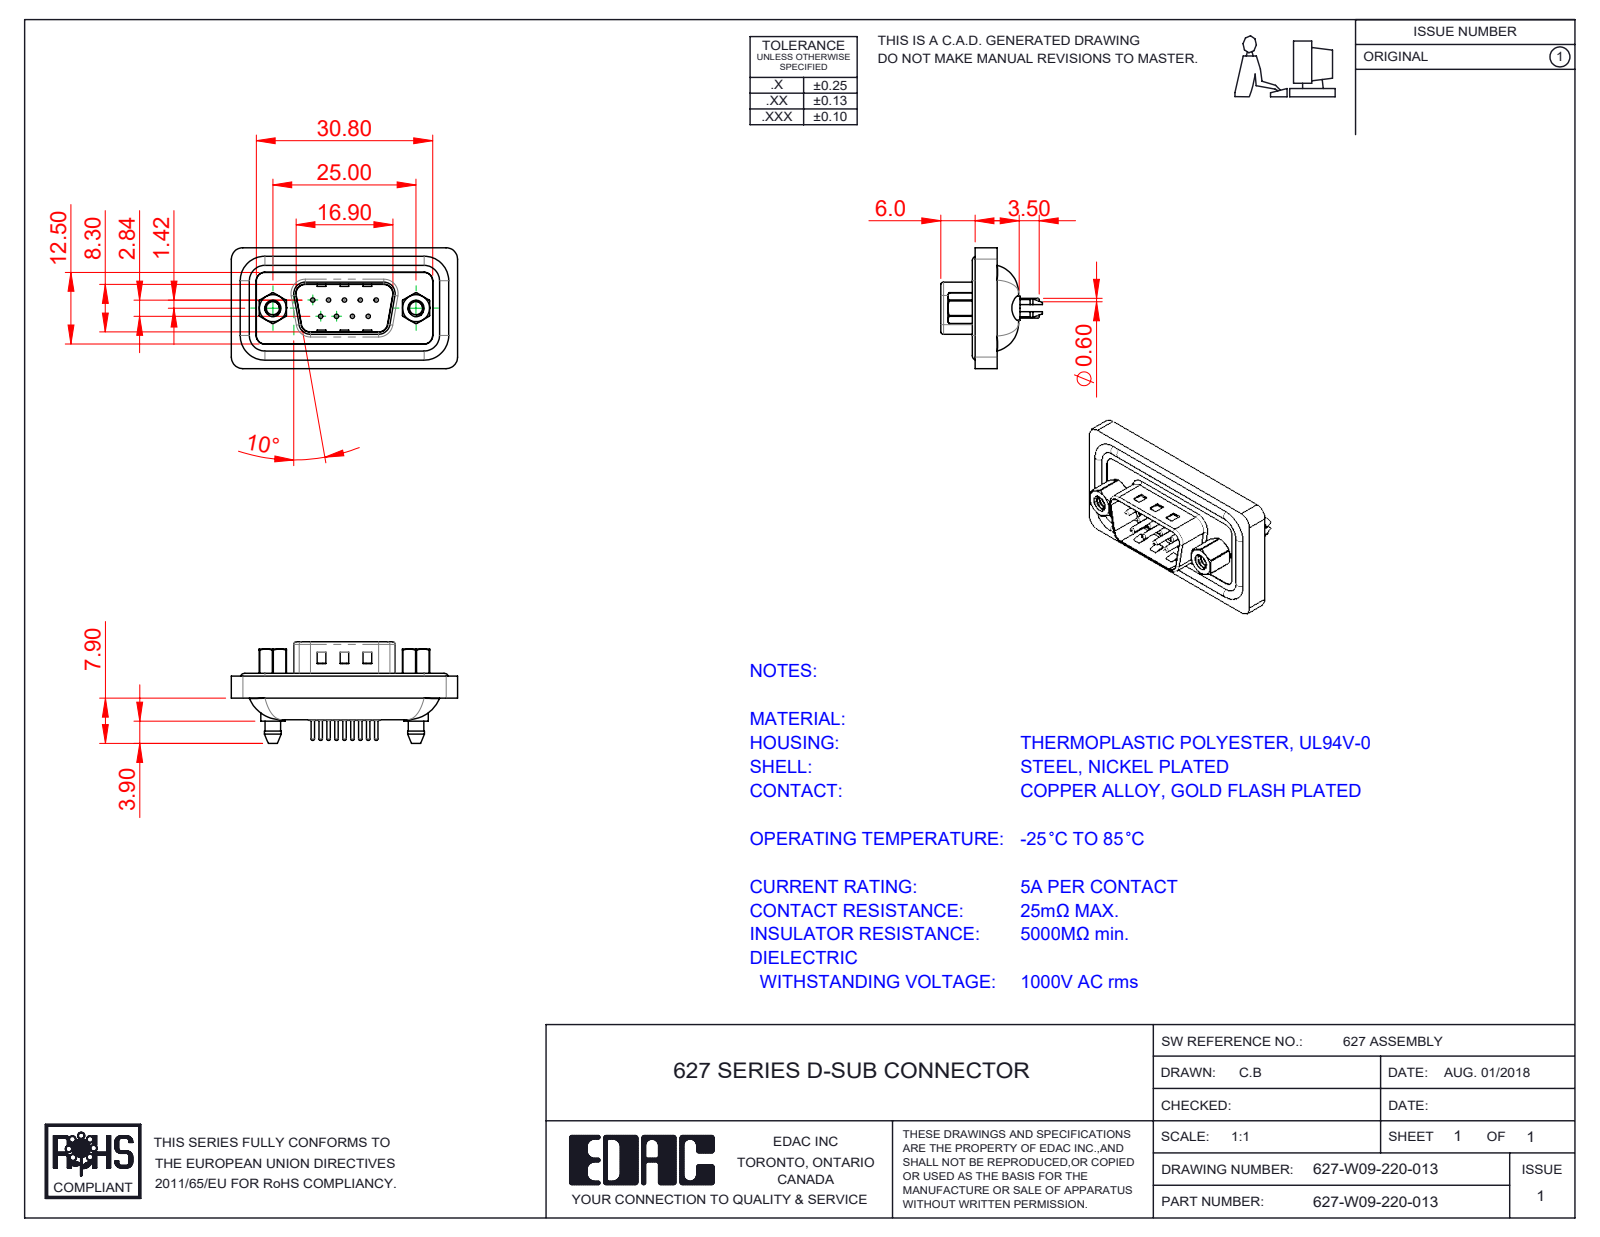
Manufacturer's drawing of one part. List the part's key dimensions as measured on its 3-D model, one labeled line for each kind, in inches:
Part name (STEP PRODUCT): 627W 4-40 Hex Standoff; 627W Contact Row 2_20; 627W Waterproof Housing_09 Contacts BL; 627W Contact Row 1_20 (+4 more)
STEP written by: SolidWorks 2020 (CONFIG_CONTROL_DESIGN)
Units: inches
Bodies: 17 solids, 847 faces (218 planar, 388 cylindrical, 241 other)
Overall size (bounding box): 1.555 × 0.831 × 0.699
Volume: 0.288 in³ · Surface area: 10.74 in²
Round holes (diameter × count): ⌀0.03 ×9, ⌀0.059 ×9, ⌀0.063 ×9, ⌀0.079 ×9, ⌀0.089 ×2, ⌀0.09 ×2, ⌀0.157 ×2, ⌀0.167 ×2, ⌀0.189 ×2
Round bosses / shafts (diameter × count): ⌀0.024 ×9, ⌀0.063 ×4, ⌀0.059 ×4, ⌀0.213 ×2, ⌀0.193 ×2, ⌀0.11 ×2
Partial cylindrical surfaces — rounded edges, fillets, slot ends (radius × count): R0.059 ×16, R0.079 ×16, R0.02 ×8, R0.063 ×6, R0.035 ×4, R0.106 ×4, R0.169 ×4, R0.016 ×2
Main face-to-face distances: 0.016, 0.03, 0.043, 0.108, 0.02, 0.148, 0.073, 0.152, 0.132, 0.039
Hole centre spacings: 0.124, 0.109, 0.218, 0.198, 0.198, 0.294, 0.295, 0.327
